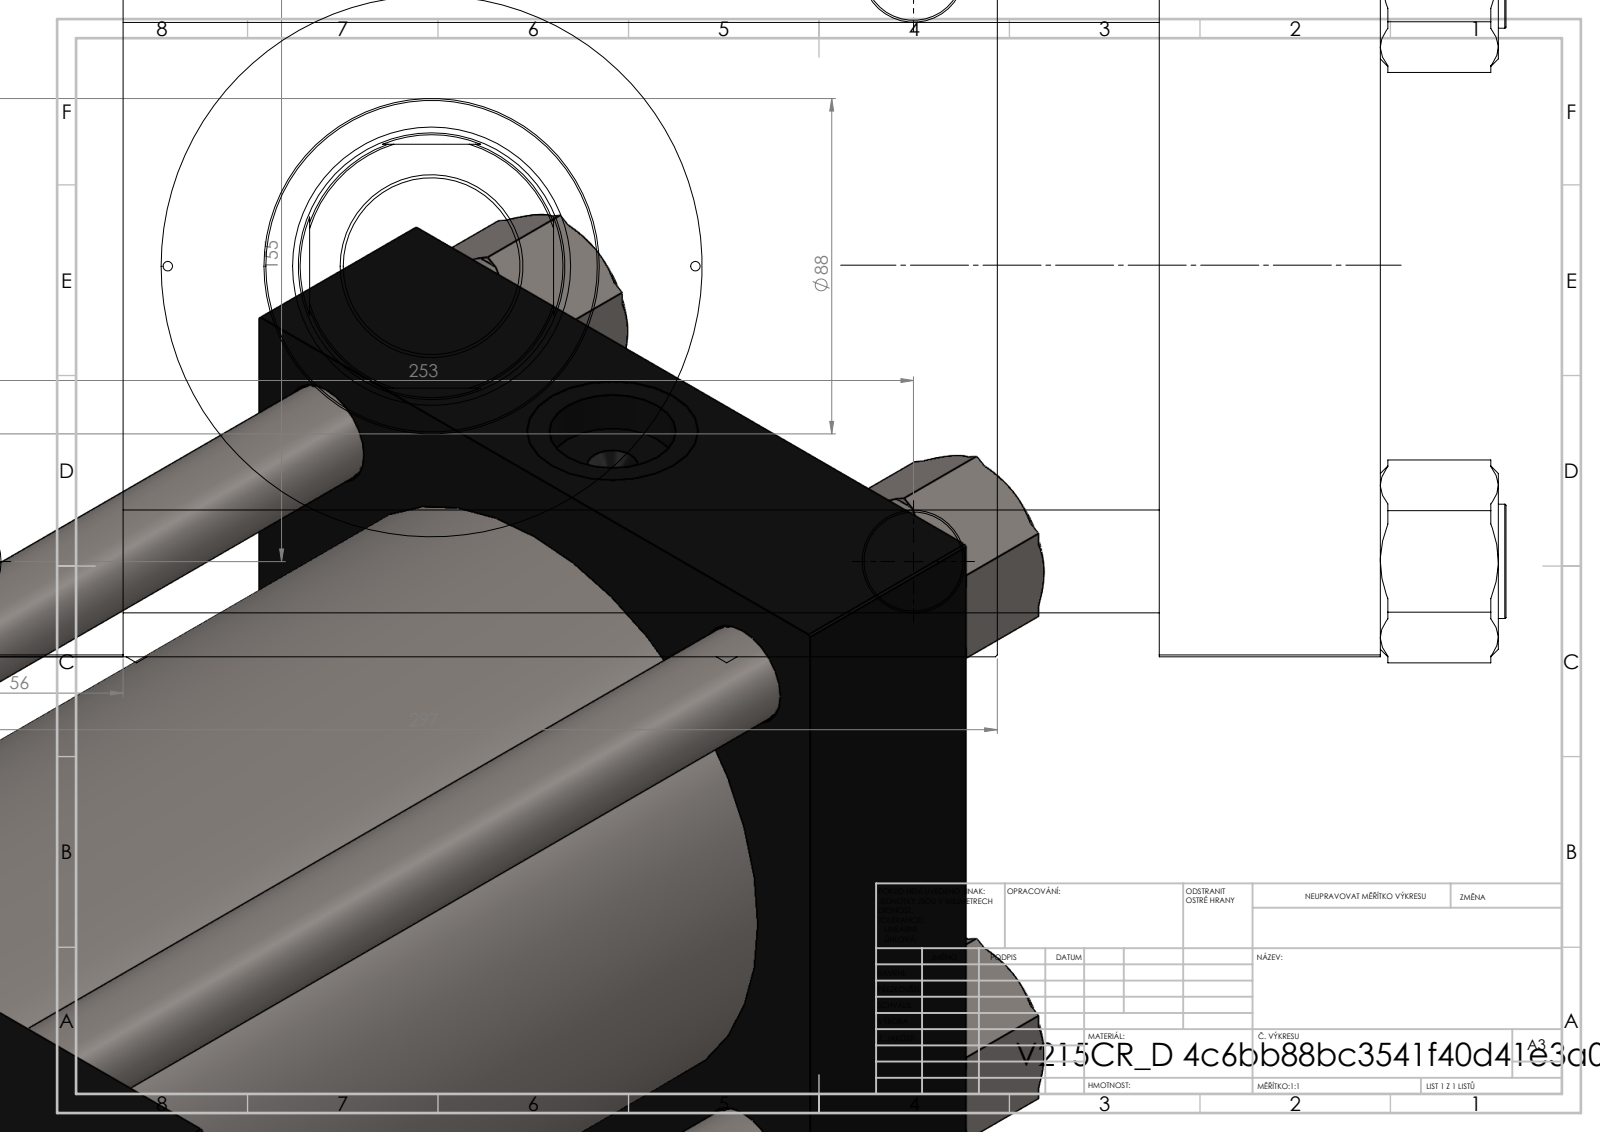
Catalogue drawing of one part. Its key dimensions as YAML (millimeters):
part_name: "V215CR_D_TYCINKA; ROD_END_AH; V215_VC_A; NUT_M5_D (+2 more)"
step_written_by: "SolidWorks 2019 (CONFIG_CONTROL_DESIGN)"
units: millimeters
bodies: {solids: 12, faces: 1169, planar: 550, cylindrical: 95, other: 524}
overall_size: [539, 297, 208.14]
volume: 9391000
surface_area: 1023000
round_holes:
  - {diameter: 26, count: 4}
  - {diameter: 27, count: 4}
  - {diameter: 2.5, count: 2}
  - {diameter: 7, count: 2}
  - {diameter: 33.24, count: 2}
  - {diameter: 45, count: 2}
  - {diameter: 46.5, count: 1}
  - {diameter: 70, count: 1}
  - {diameter: 73, count: 1}
  - {diameter: 120, count: 1}
  - {diameter: 142, count: 1}
  - {diameter: 160, count: 1}
round_bosses_or_shafts:
  - {diameter: 30, count: 4}
  - {diameter: 166, count: 1}
  - {diameter: 88, count: 1}
  - {diameter: 48, count: 1}
  - {diameter: 46, count: 1}
partial_cylinders:
  - {radius: 34, count: 1}
face_to_face_distances: [58, 330, 272, 386, 328, 56, 205, 46, 251, 72]
hole_center_spacings: [49.05, 77.88, 96.35, 109.53, 148.35, 154.9, 162.53, 165.89]
